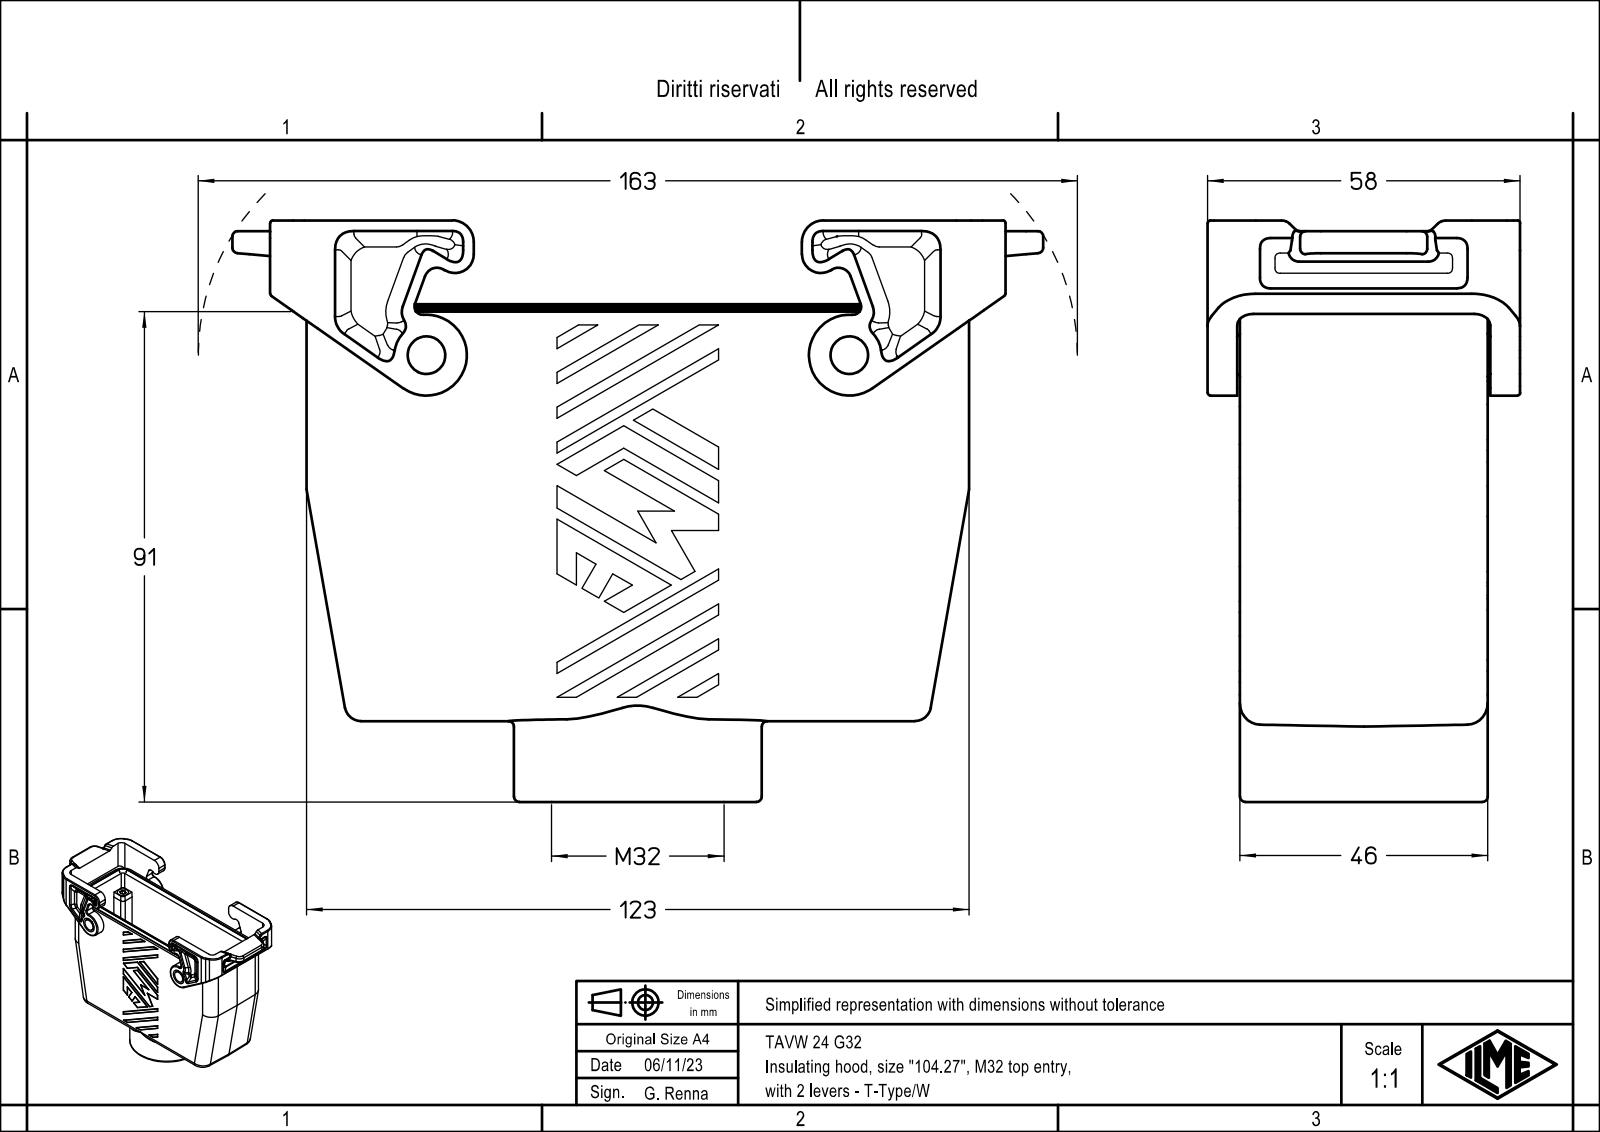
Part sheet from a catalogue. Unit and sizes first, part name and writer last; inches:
Units: inches
Overall size (bounding box): 5.925 × 4.248 × 2.283
Round holes (diameter × count): ⌀1.102 ×1, ⌀1.205 ×1
Round bosses / shafts (diameter × count): ⌀0.276 ×2, ⌀1.811 ×1
Partial cylindrical surfaces — rounded edges, fillets, slot ends (radius × count): R0.006 ×88, R0.118 ×20, R0.039 ×16, R0.079 ×16, R0.059 ×10, R0.051 ×8, R0.236 ×8, R0.276 ×8
Main face-to-face distances: 0.213, 1.598, 1.386, 1.811, 0.02, 0.232, 1.618, 1.831, 0.217, 2.047
Volume: 11.46 in³ · Surface area: 110 in²
Bodies: 1 solid, 562 faces (218 planar, 282 cylindrical, 62 other)
Part name (STEP PRODUCT): TAVW 24 G32
STEP written by: Creo Elements/Direct Modeling 20.1B 02-Apr-2019 (C) Parametric Technology GmbH (AUTOMOTIVE_DESIGN)
